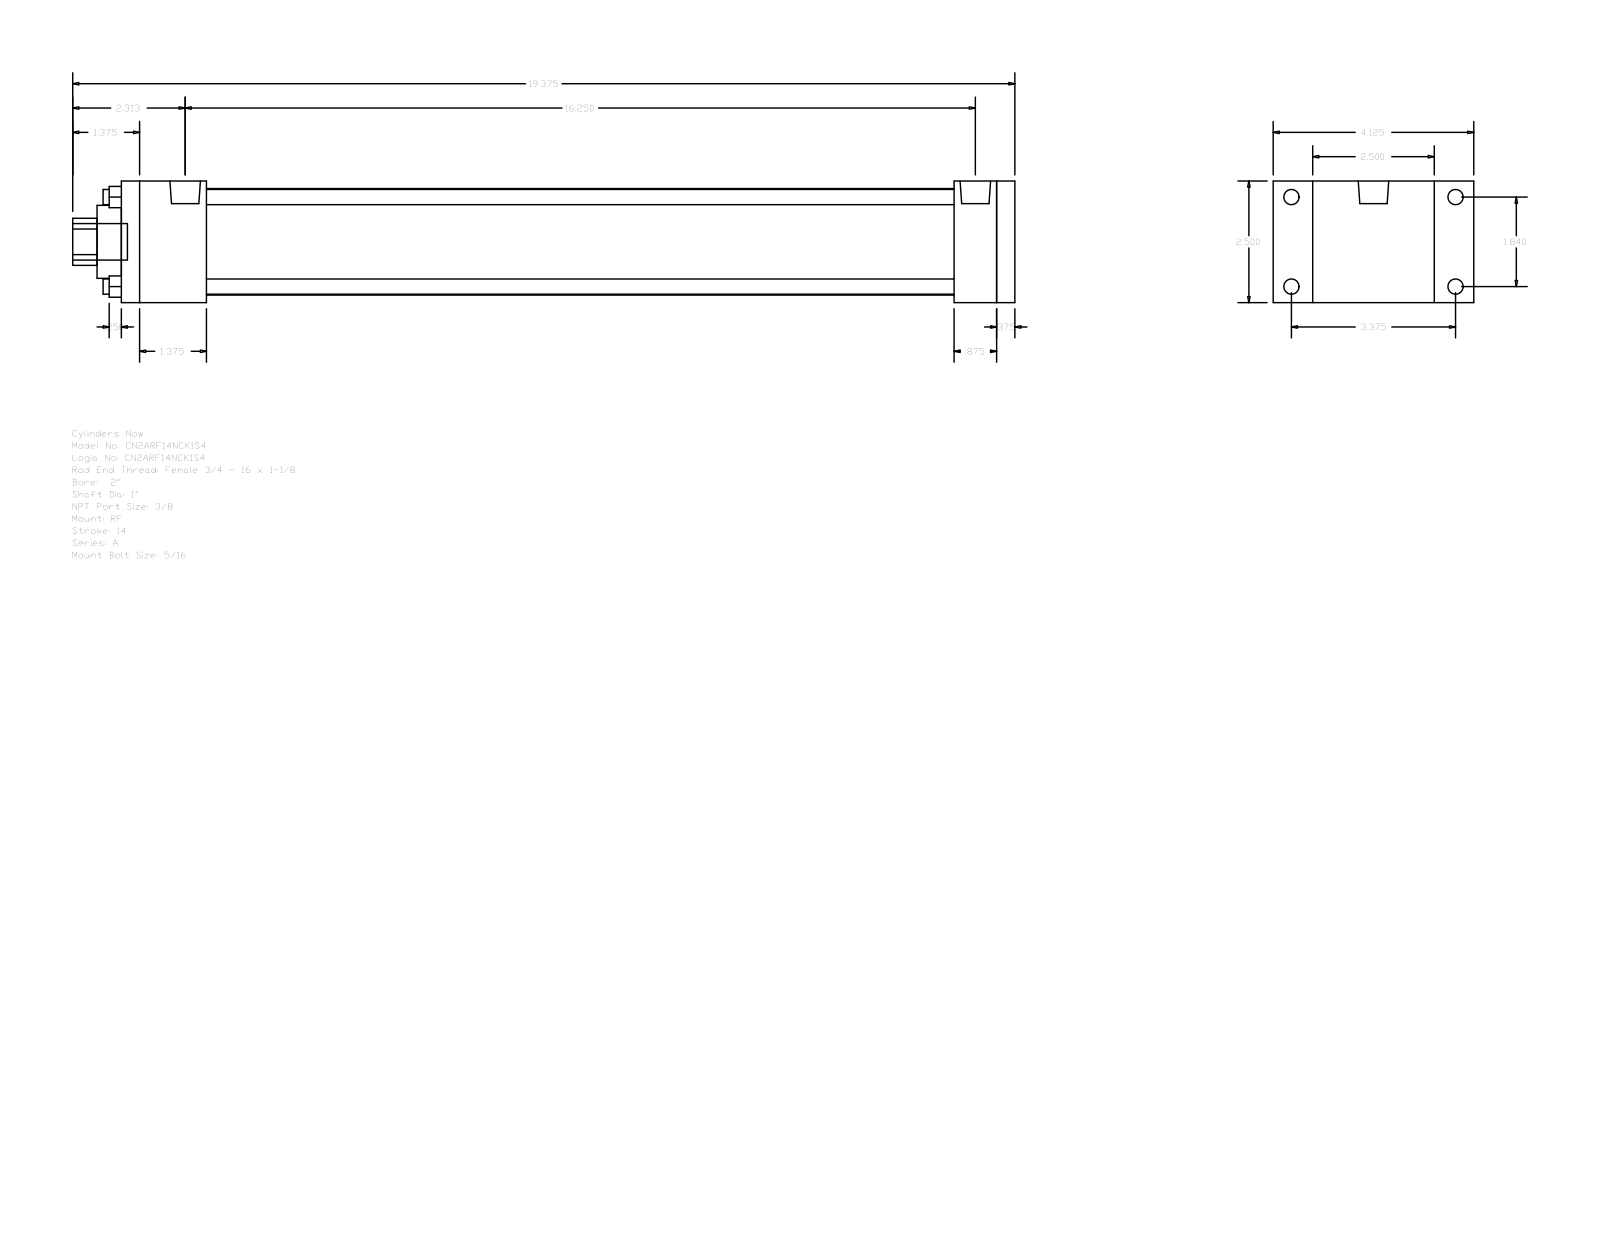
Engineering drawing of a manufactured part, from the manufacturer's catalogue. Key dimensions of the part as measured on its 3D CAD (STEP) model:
Part name (STEP PRODUCT): A_RF__0200_1
STEP written by: GSSL Pune (CONFIG_CONTROL_DESIGN)
Units: millimetres
Bodies: 0 solids, 92 faces (64 planar, 28 cylindrical, 0 other)
Overall size (bounding box): 492.12 × 104.78 × 63.5
Round holes (diameter × count): ⌀7.94 ×4, ⌀25.4 ×1, ⌀38.1 ×1, ⌀55.63 ×1
Round bosses / shafts (diameter × count): ⌀7.94 ×4, ⌀5.56 ×4, ⌀15.93 ×2, ⌀19.05 ×1
Partial cylindrical surfaces — rounded edges, fillets, slot ends (radius × count): R12.29 ×1
Main face-to-face distances: 63.5, 9.52, 466.72, 457.2, 20.64, 44.45, 412.75, 422.27, 434.98, 390.53
Hole centre spacings: 33.05, 46.74, 66.1
